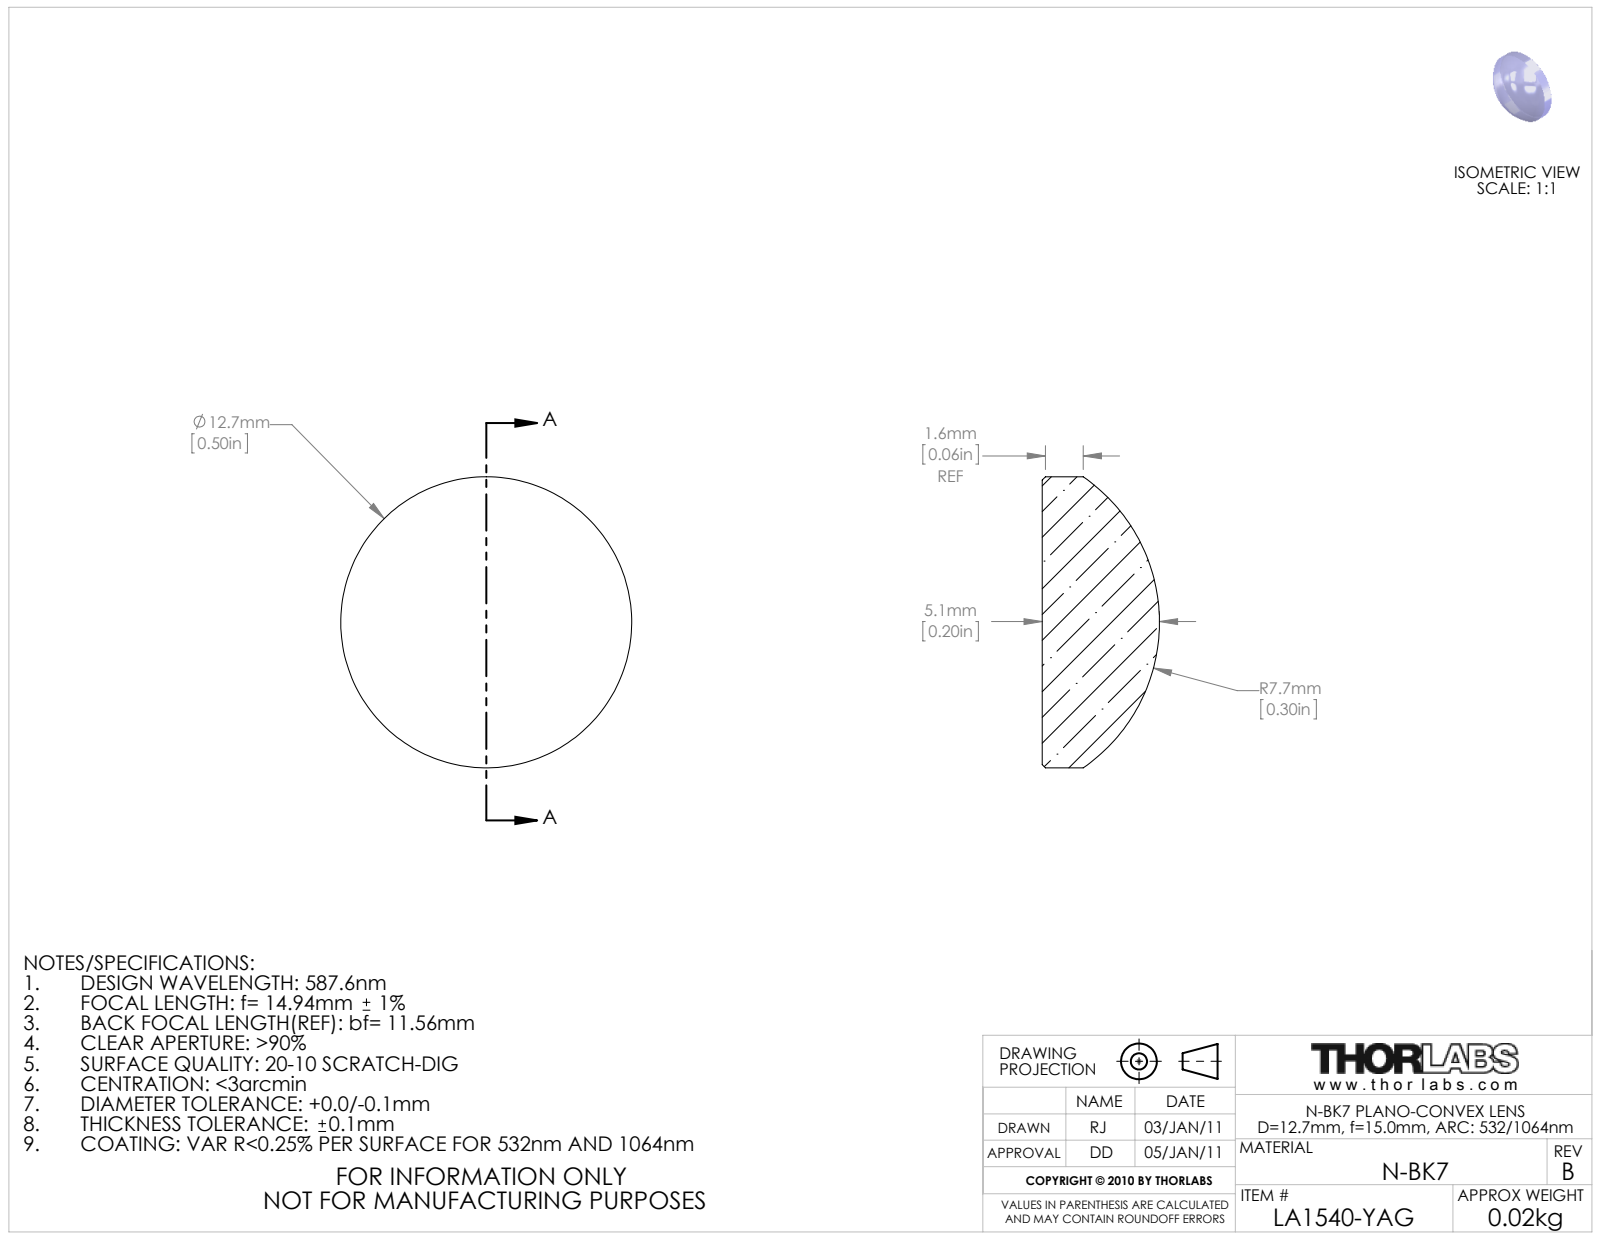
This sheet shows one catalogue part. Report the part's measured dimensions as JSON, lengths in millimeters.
{"part_name": "21773-E0W", "step_written_by": "SolidWorks 2011 (AUTOMOTIVE_DESIGN)", "units": "millimeters", "bodies": {"solids": 0, "faces": 7, "planar": 1, "cylindrical": 2, "other": 4}, "overall_size": [12.7, 12.7, 5.12], "round_bosses_or_shafts": [[12.7, 1]]}
